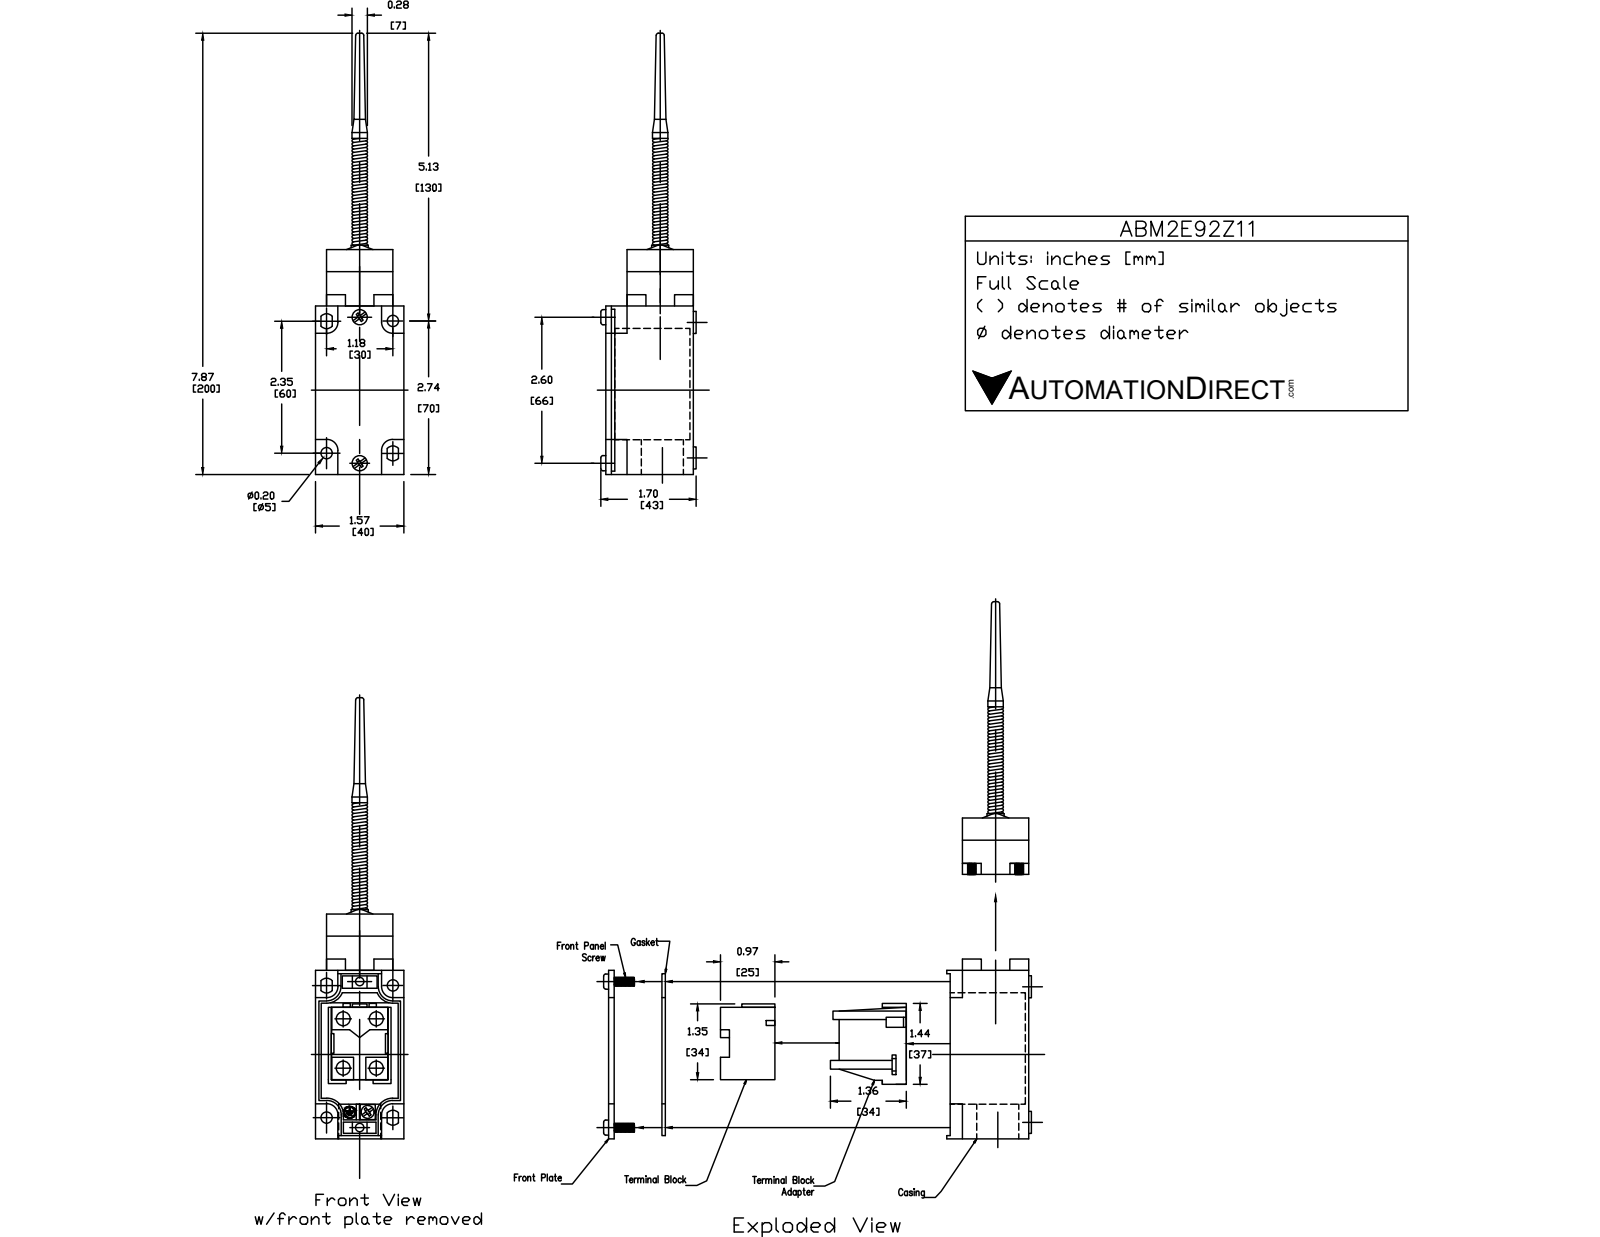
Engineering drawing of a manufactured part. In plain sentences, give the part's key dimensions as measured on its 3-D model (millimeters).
The part is named "ABM2E92Z11". Its 3-D file was written by "SolidWorks 2017 (AUTOMOTIVE_DESIGN)". It is 3 solids with 201 faces: 79 planar, 84 cylindrical and 38 other. Overall it measures 197.8 by 43.3 by 40 millimeters. Its volume is 129 600 cubic millimeters and its surface area 24 980 square millimeters. Round holes: 2 of diameter 5.2, 1 of diameter 17, 1 of diameter 19, 1 of diameter 20.5. Round bosses or shafts: 6 of diameter 7, 4 of diameter 10, 1 of diameter 19, 1 of diameter 11.7, 1 of diameter 6.8. Partial cylindrical surfaces (rounded edges, fillets, slot ends): 16 of radius 1.5, 4 of radius 0.5, 4 of radius 0.6, 4 of radius 5, 2 of radius 3.3, 1 of radius 11.5, 1 of radius 12. The main face-to-face distances are 40, 39.5, 30, 5, 76.5, 9.5, 35, 77, 0.5, 81.5. The hole center spacings are 1, 67.1.
